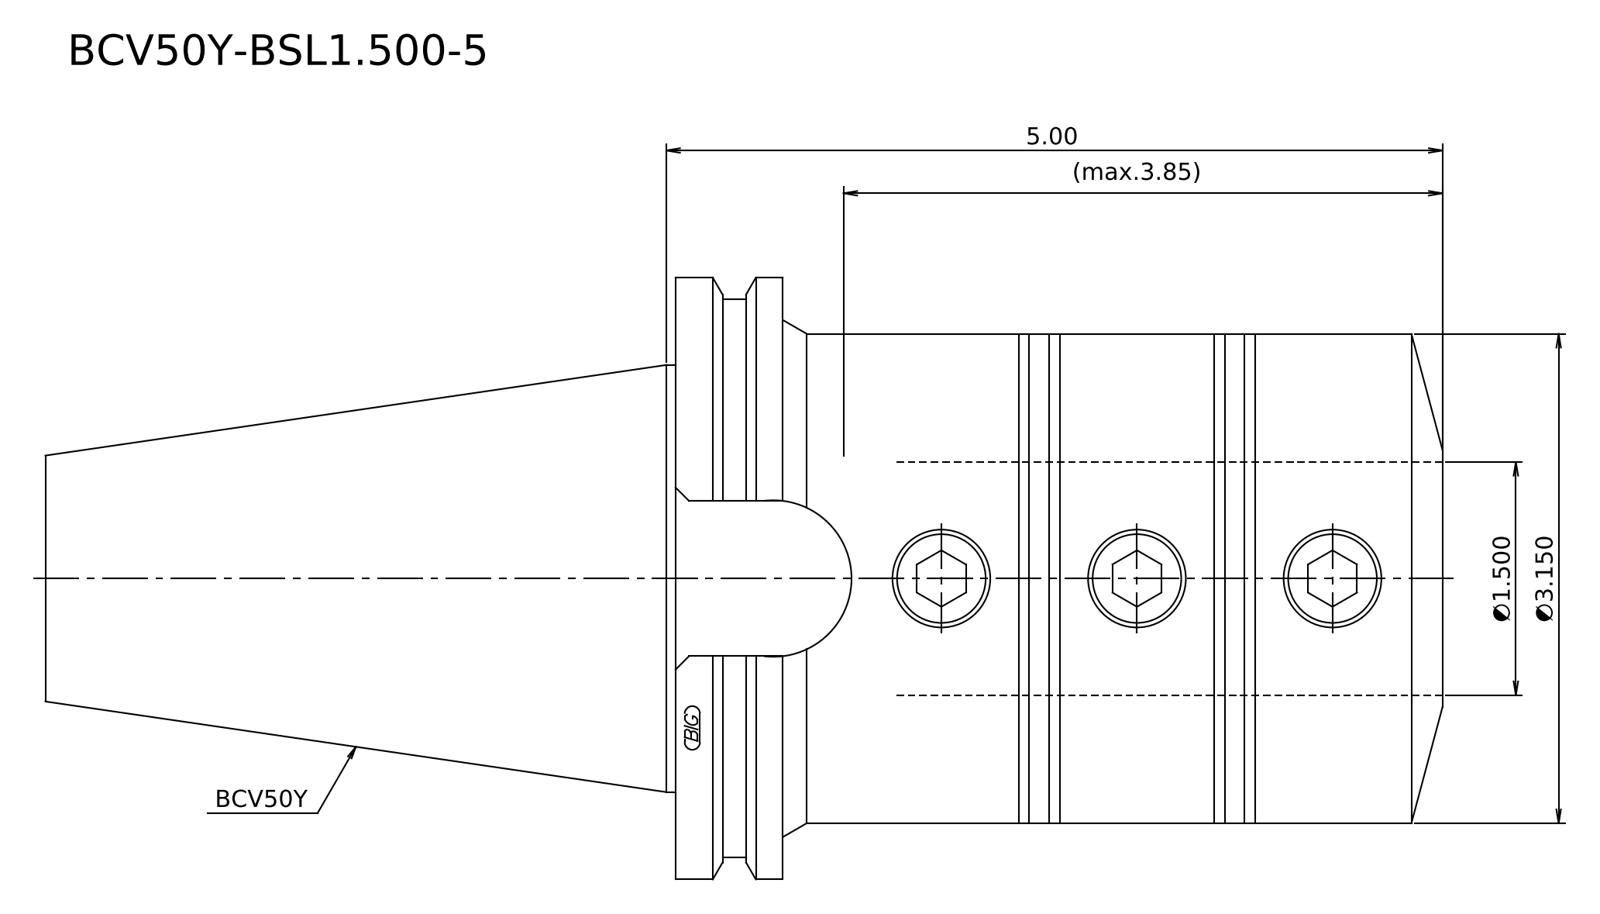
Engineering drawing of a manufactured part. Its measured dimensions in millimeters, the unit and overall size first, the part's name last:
Units: millimetres
Overall size (bounding box): 228.6 × 98.42 × 98.42
Round bosses / shafts (diameter × count): ⌀98.42 ×1, ⌀91.29 ×1, ⌀80 ×1, ⌀69.85 ×1
Main face-to-face distances: 17.55, 107.95, 125.5, 228.6, 120.65, 103.1, 113.96, 6.01, 11.54, 114.64
Volume: 914 894 mm³ · Surface area: 63 045 mm²
Bodies: 1 solid, 16 faces (6 planar, 5 cylindrical, 5 other)
STEP written by: Kubotek KeyCreator 2011 V10.0.2 (22737) (automotive_design)
